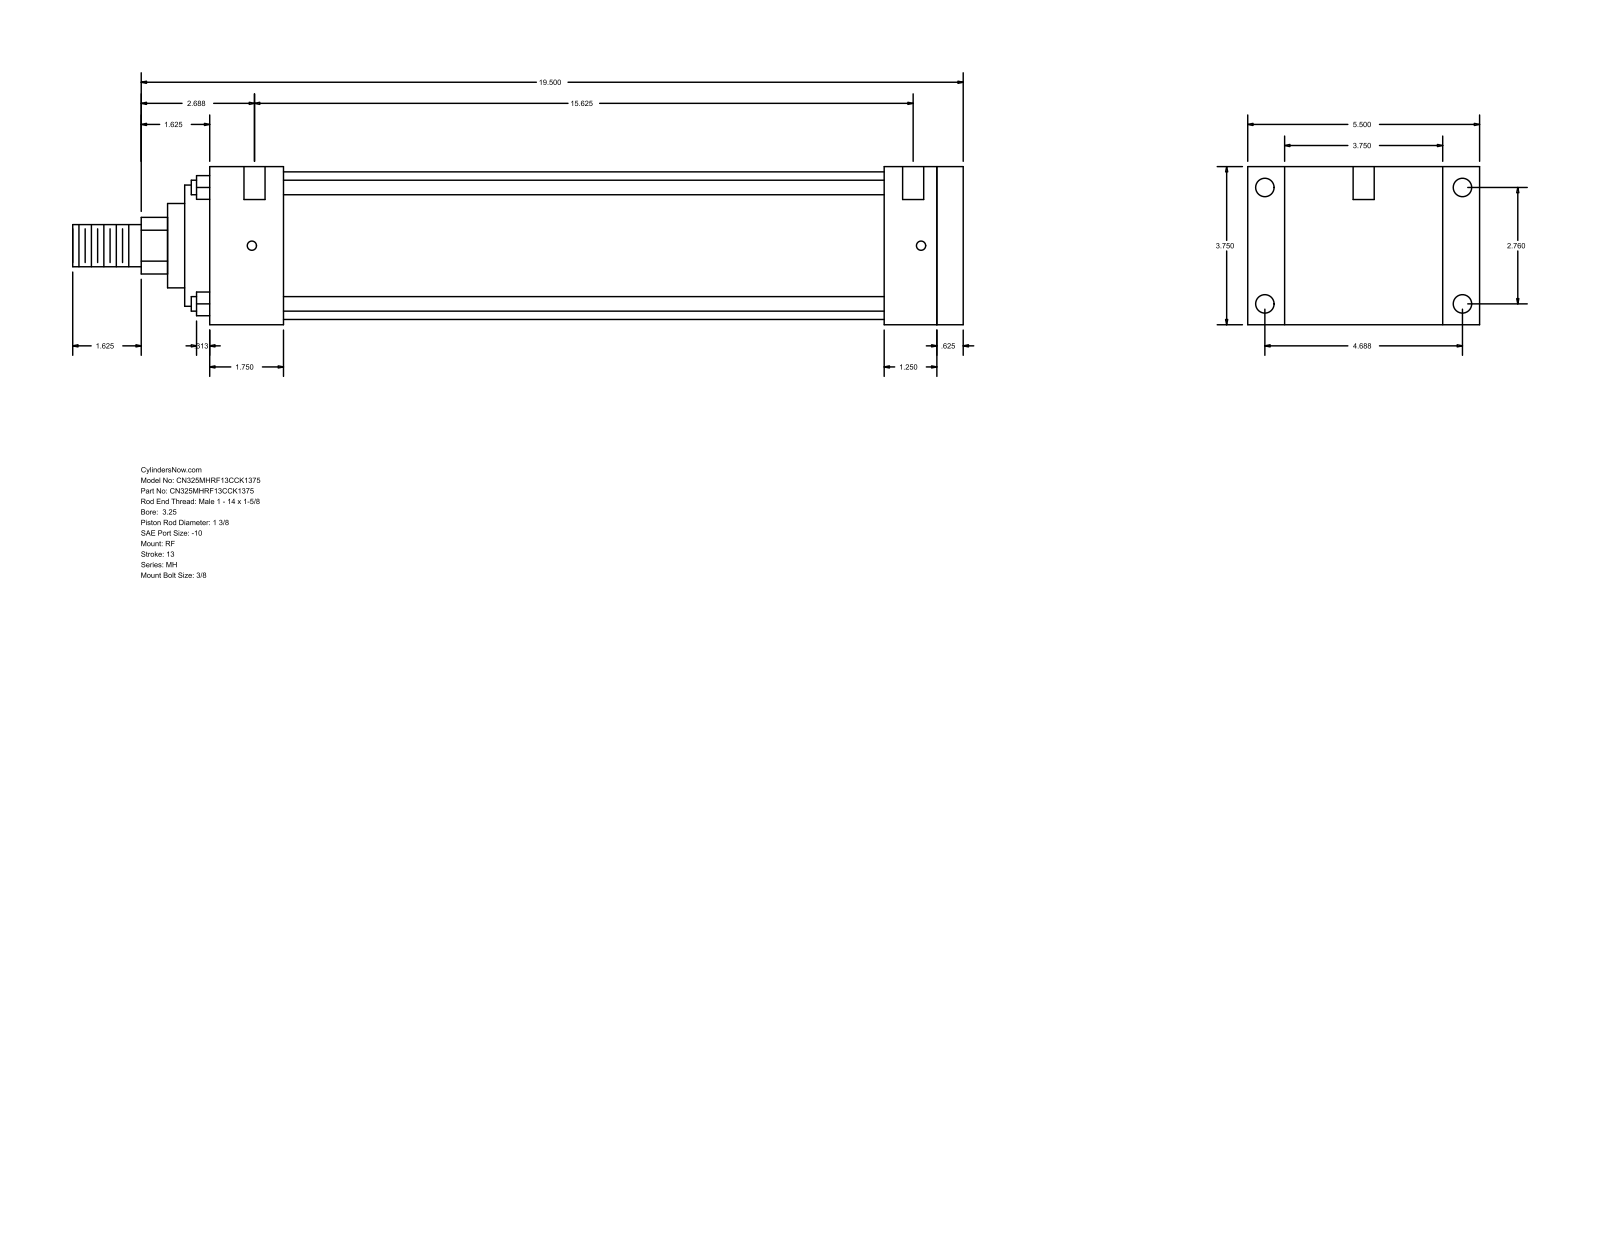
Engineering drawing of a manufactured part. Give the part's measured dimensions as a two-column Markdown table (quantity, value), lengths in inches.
| quantity | value |
| --- | --- |
| part name | MH_RF__0325_1.375 |
| STEP written by | GSSL Pune (CONFIG_CONTROL_DESIGN) |
| units | inches |
| bodies | 0 solids, 94 faces (65 planar, 29 cylindrical, 0 other) |
| overall size | 21.125 × 5.5 × 3.75 |
| round holes (diameter × count) | 0.219 × 4, 0.438 × 4, 0.5 × 2 |
| round bosses / shafts (diameter × count) | 0.345 × 4, 3.5 × 1, 2.875 × 1, 2 × 1, 1.375 × 1, 1 × 1 |
| partial cylindrical surfaces (radius × count) | 0.672 × 1 |
| main face-to-face distances | 3.75, 17.875, 17.25, 0.625, 0.875, 4.625, 1.75, 15.5, 16.125, 16 |
| hole center spacings | 2.76, 4.687, 5.439, 15.875, 0.063, 0.187, 15.625, 15.688 |
